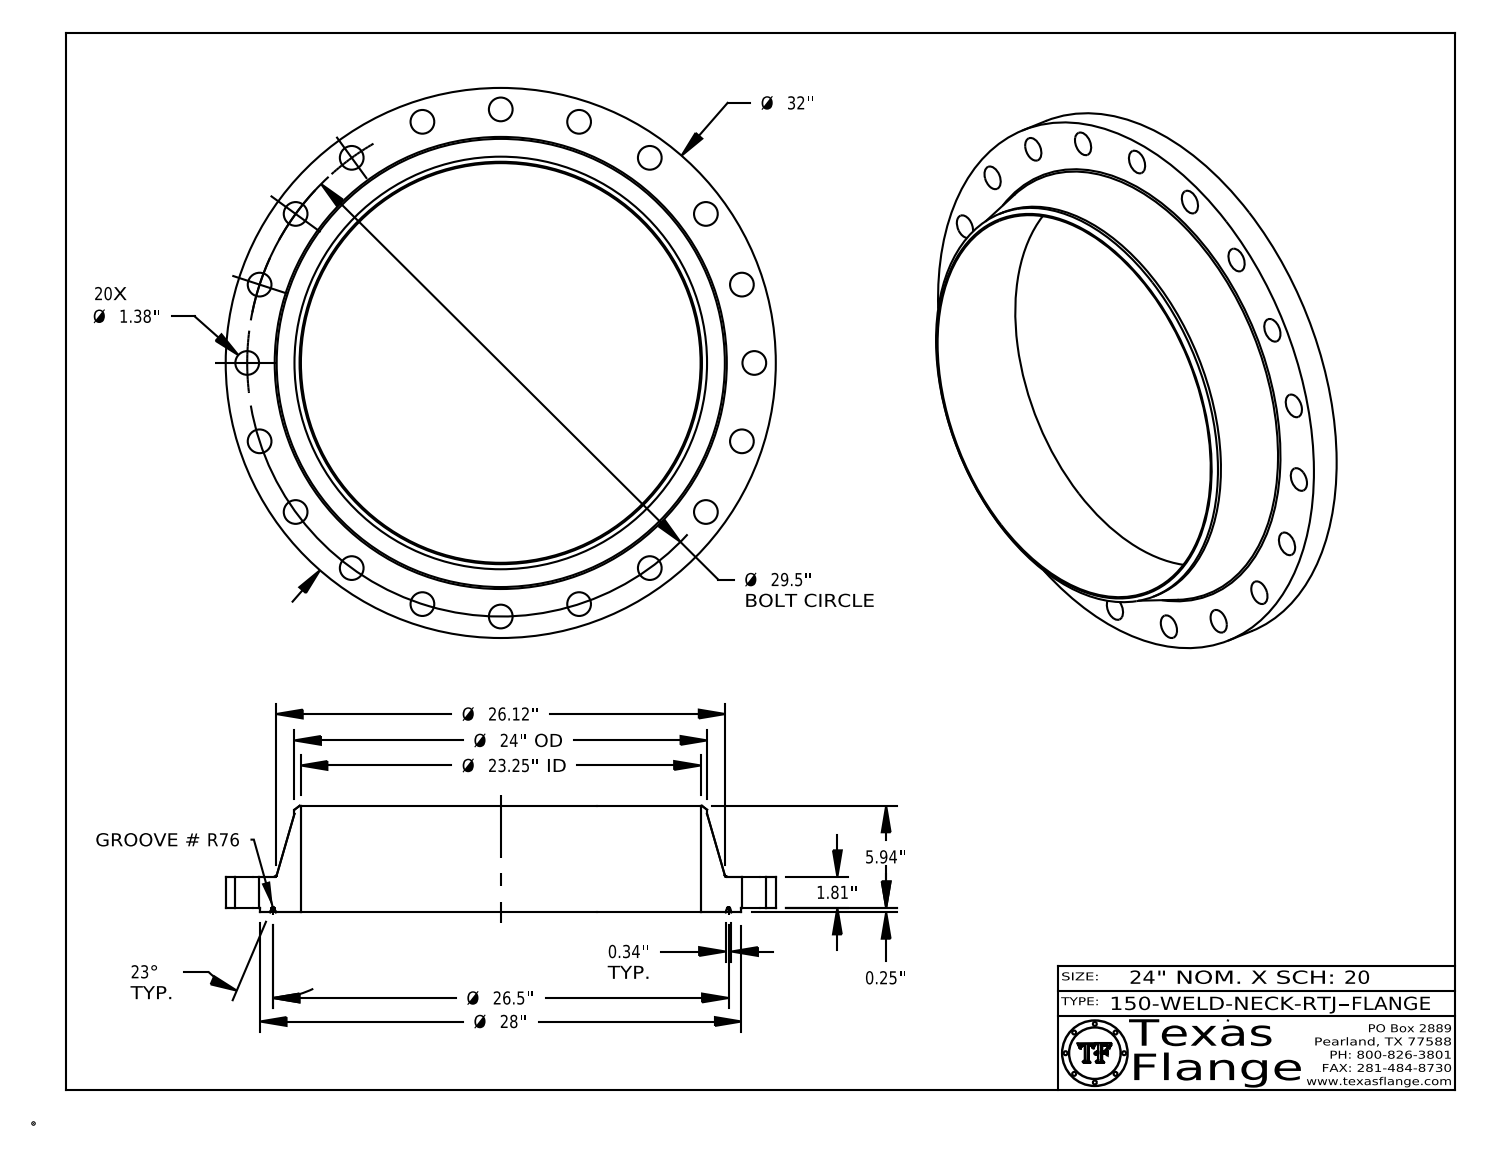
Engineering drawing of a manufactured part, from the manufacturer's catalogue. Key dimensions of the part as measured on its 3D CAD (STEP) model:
Part name (STEP PRODUCT): 150-WELD-NECK-RTJ
STEP written by: CATIA V5 STEP AP214 (AUTOMOTIVE_DESIGN)
Units: inches
Bodies: 1 solid, 453 faces (371 planar, 68 cylindrical, 14 other)
Overall size (bounding box): 32 × 32 × 6.19
Volume: 939.3 in³ · Surface area: 1 778 in²
Round holes (diameter × count): ⌀1.38 ×20, ⌀0.495 ×1, ⌀23.25 ×1
Round bosses / shafts (diameter × count): ⌀0.03 ×8, ⌀32 ×1, ⌀28 ×1, ⌀24 ×1, ⌀0.39 ×1
Main face-to-face distances: 1.81, 0.25, 2.06, 6.19, 5.94, 4.13, 2.055, 1.805, 4.135, 0.148
Hole centre spacings: 14.75, 29.137, 4.615, 17.34, 20.859, 23.866, 26.285, 9.116
